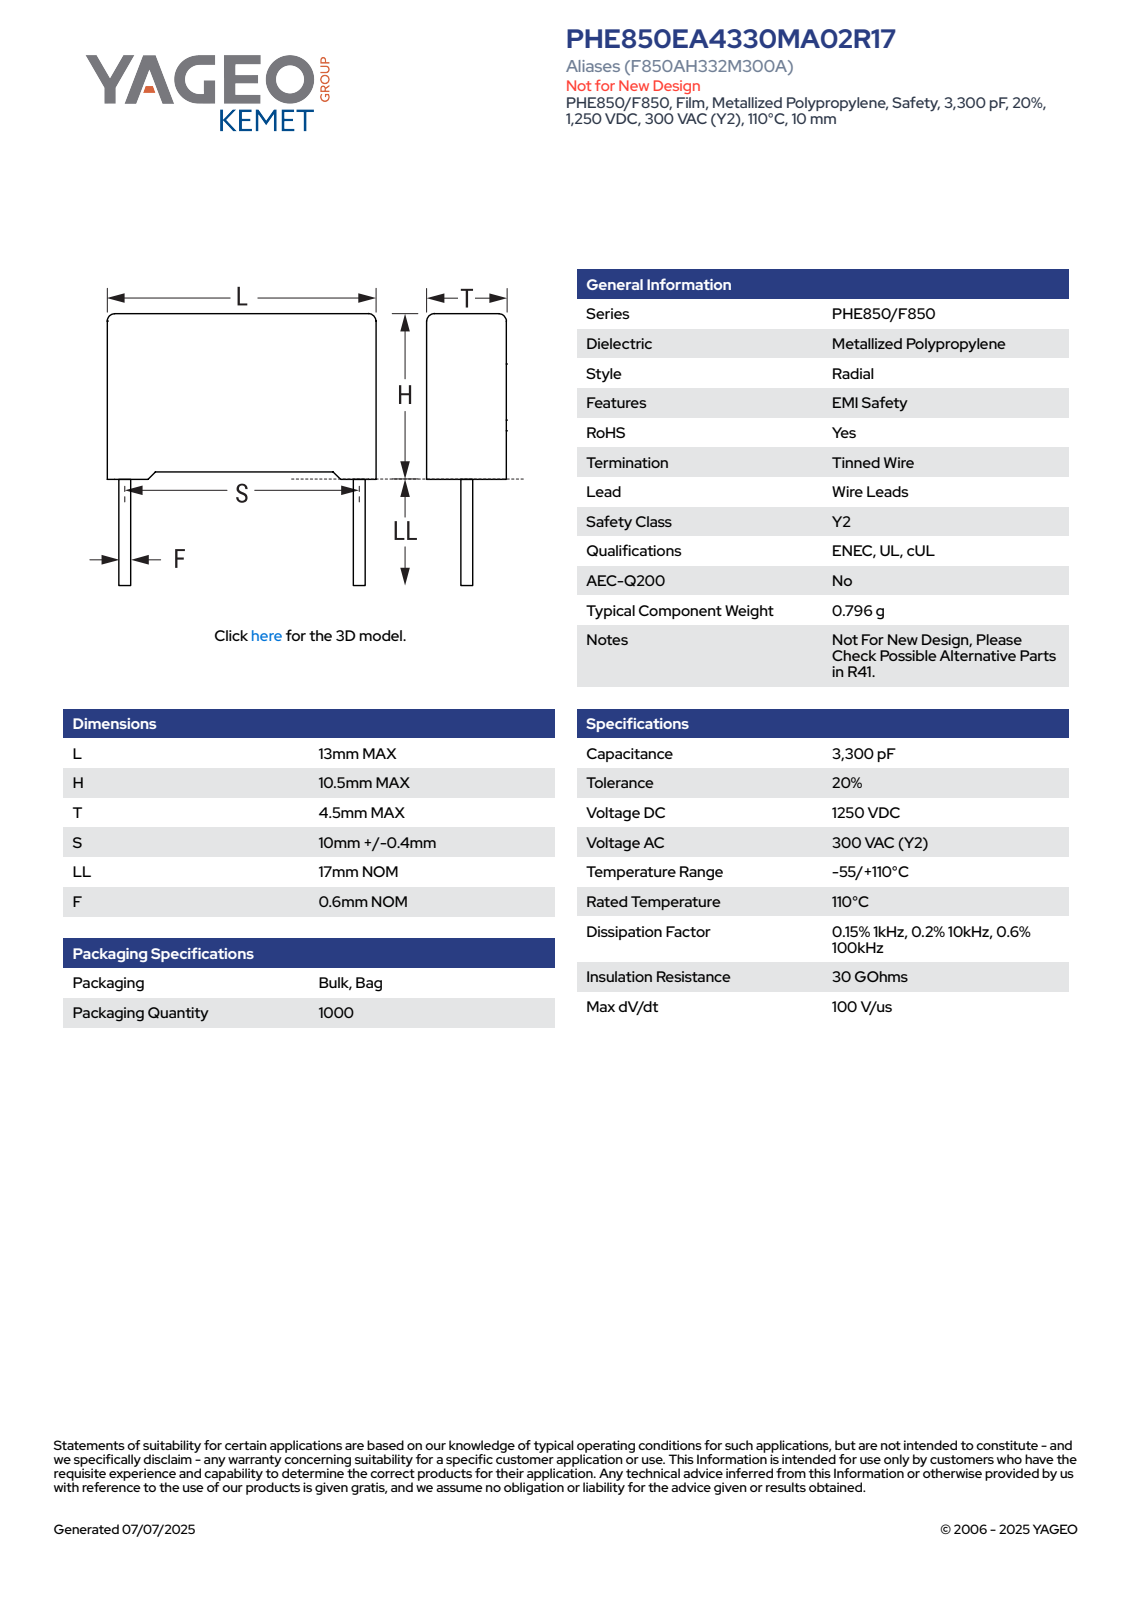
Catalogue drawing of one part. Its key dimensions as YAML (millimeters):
part_name: "CFR_RB2_13X10.5X4.5_L13H10.5T4.5S10LL17F0.6"
step_written_by: "SolidWorks 2021 (AUTOMOTIVE_DESIGN)"
units: millimeters
bodies: {solids: 4, faces: 85, planar: 77, cylindrical: 8, other: 0}
overall_size: [27.5, 13, 4.5]
volume: 587
surface_area: 571
round_bosses_or_shafts:
  - {diameter: 0.6, count: 2}
partial_cylinders:
  - {radius: 0.5, count: 4}
face_to_face_distances: [4.5, 13, 9.75, 0.43, 4.07, 0.75, 10.5, 3.64, 0.36, 12.57]
